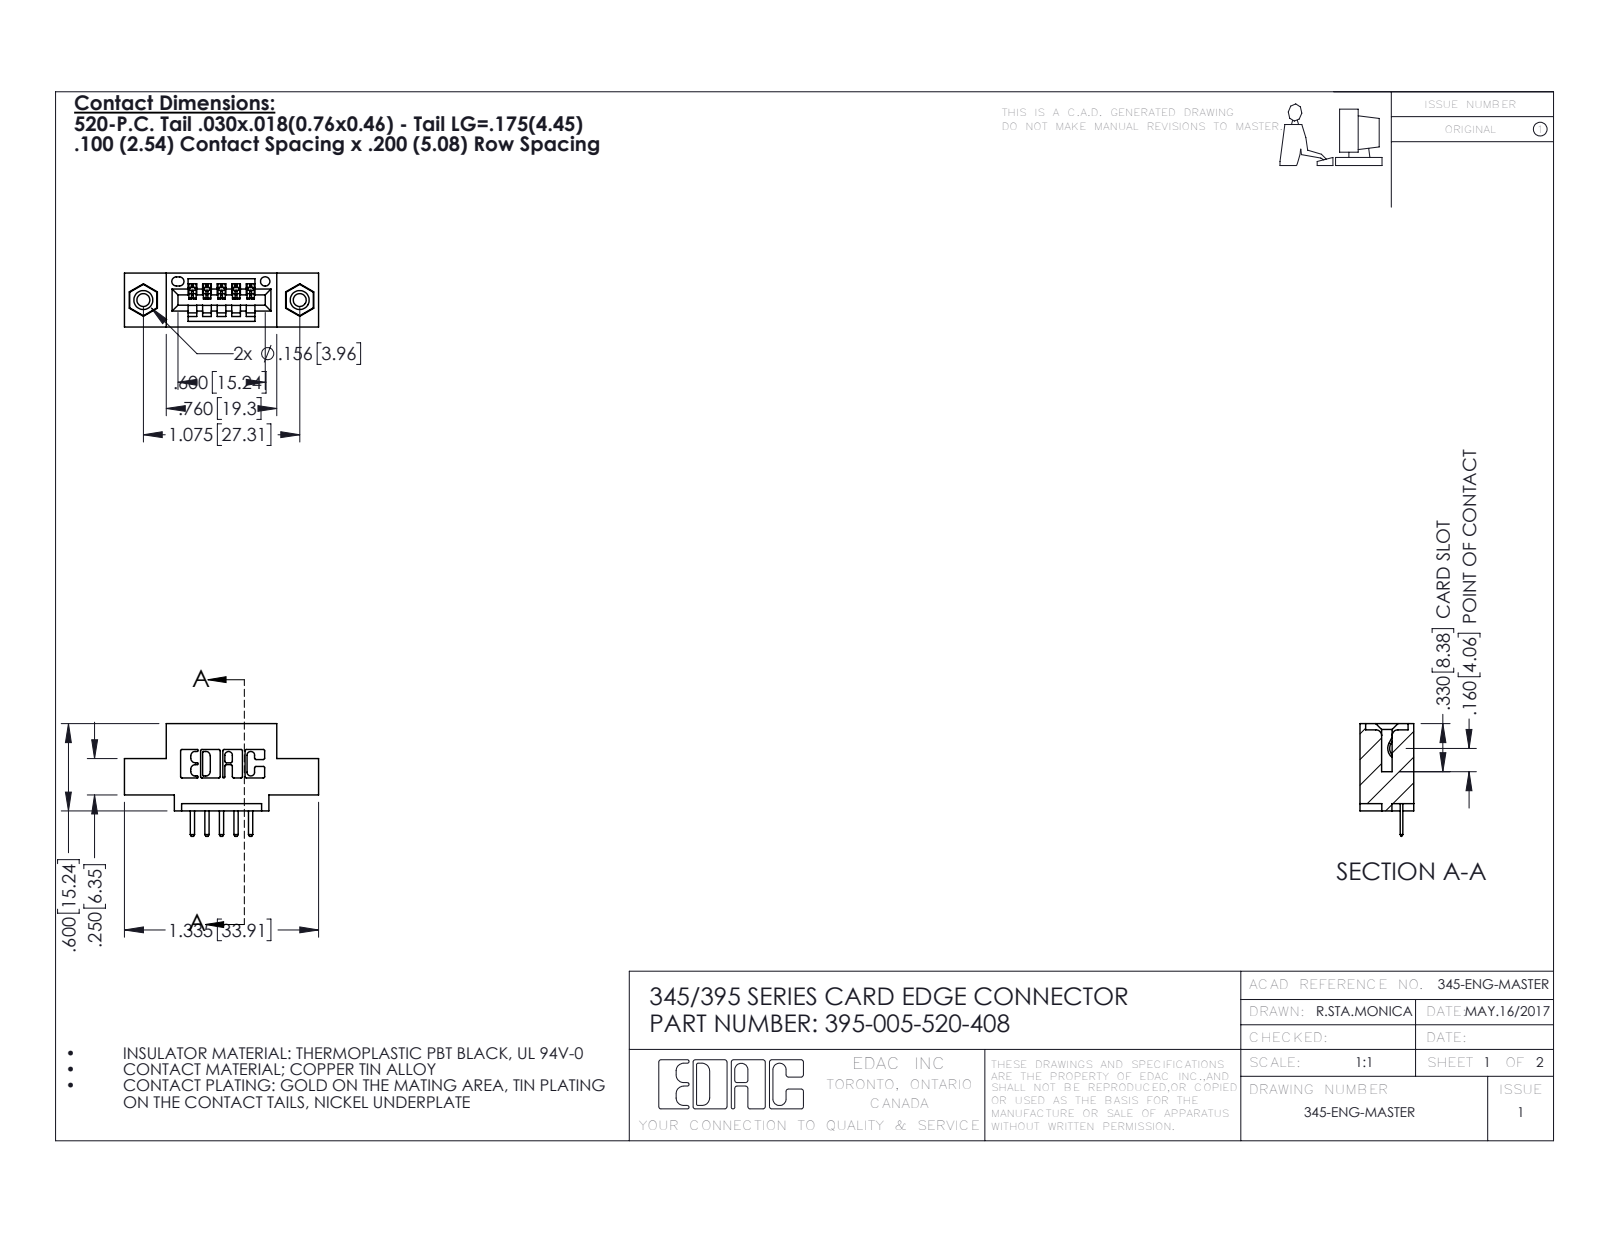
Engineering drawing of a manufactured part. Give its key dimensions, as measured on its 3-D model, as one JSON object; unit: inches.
{"part_name": "345-250-001_345-250-003-102; 345-292-001_345-293-120; 395-005-520-408; 345 Part_0.110 Offset - 0.156 Dia-TI", "step_written_by": "SolidWorks 2016 (CONFIG_CONTROL_DESIGN)", "units": "inches", "bodies": {"solids": 8, "faces": 500, "planar": 326, "cylindrical": 158, "other": 16}, "overall_size": [1.335, 0.775, 0.37], "volume_in3": 0.172, "surface_area_in2": 5.12, "round_holes": [[0.089, 2], [0.125, 2], [0.156, 2], [0.064, 1]], "round_bosses_or_shafts": [[0.155, 2]], "partial_cylinders_radius": [[0.01, 22], [0.01, 12], [0.006, 10], [0.007, 6], [0.031, 6], [0.026, 3], [0.031, 2], [0.04, 2]], "face_to_face_distances": [0.2, 0.37, 0.1, 0.072, 0.298, 0.025, 0.25, 0.06, 0.16, 0.04], "hole_center_spacings": [0.27, 0.847, 1.075]}
